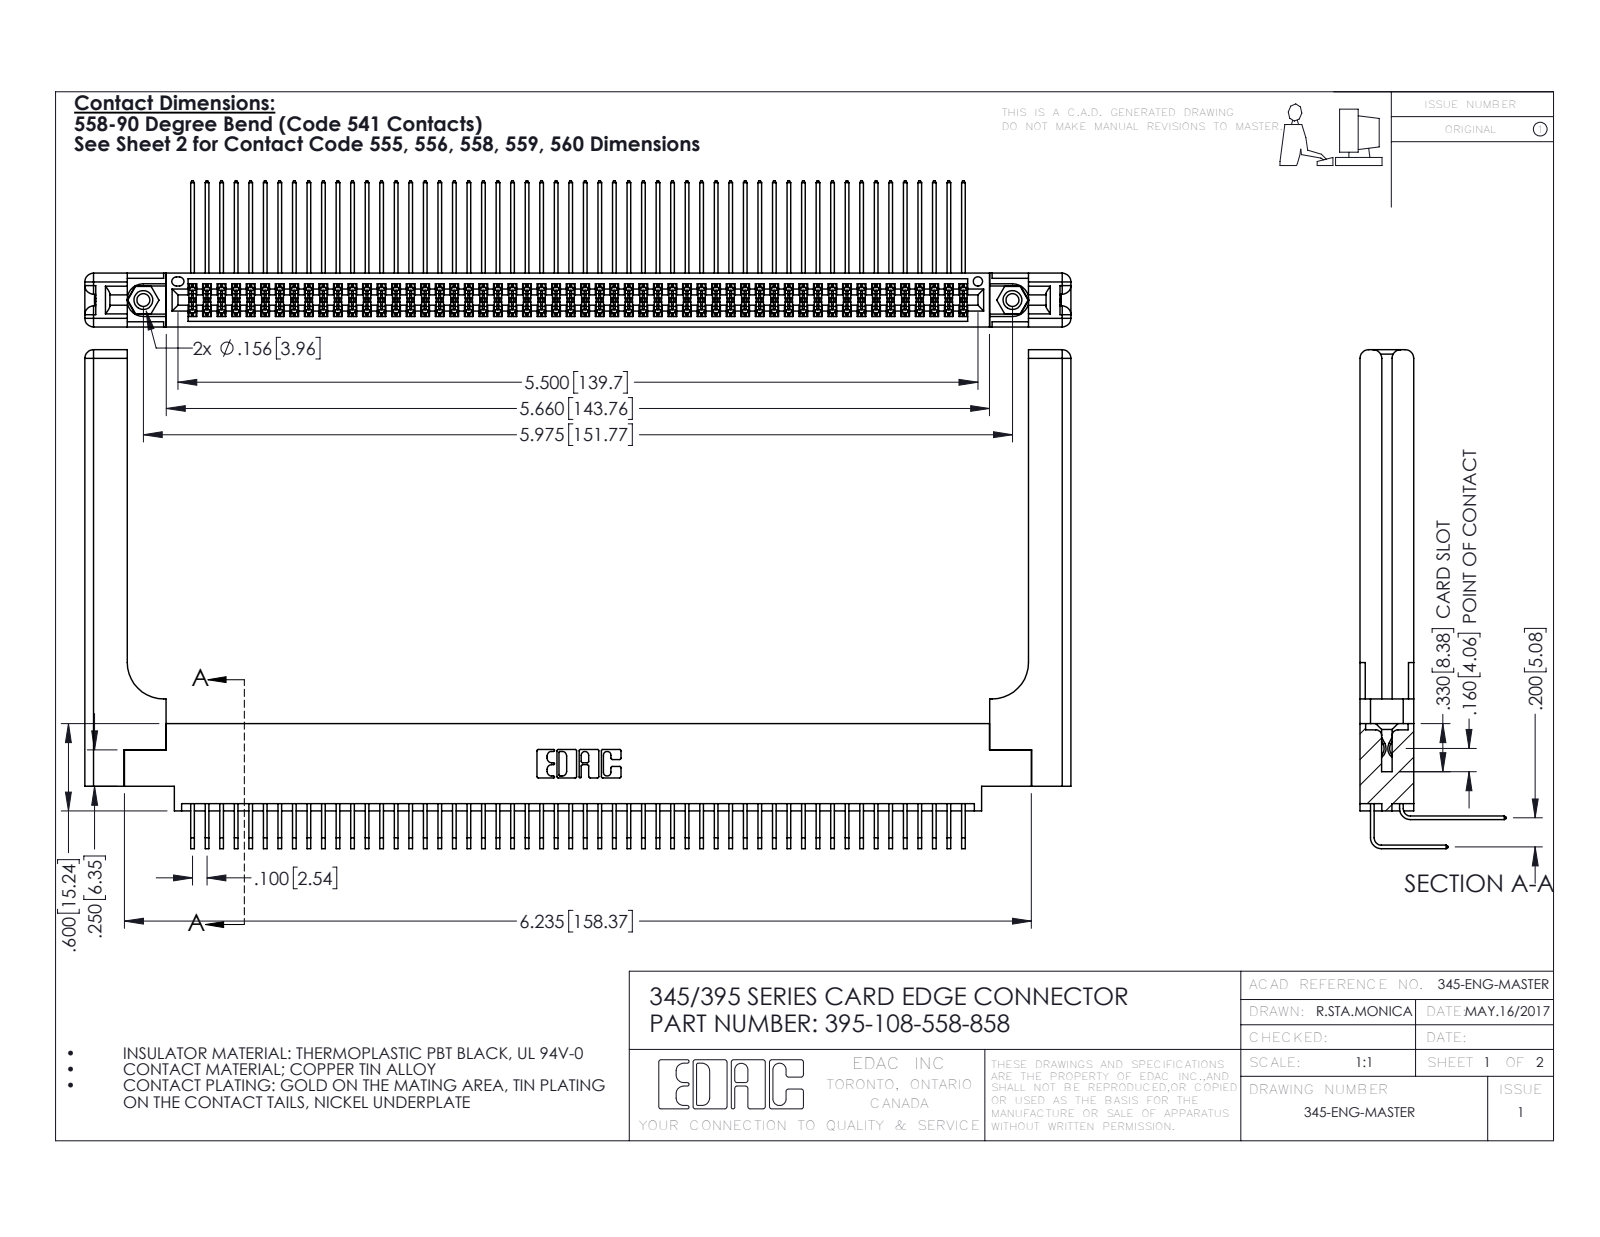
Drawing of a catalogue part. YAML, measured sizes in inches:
part_name: "395-108-558-858; 345-250-001_345-250-001-102; 345 Part_0.170 Offset - 0.156 Dia-TH; 345-292-001_558 559 Tail - 1 (+2 more)"
step_written_by: "SolidWorks 2016 (CONFIG_CONTROL_DESIGN)"
units: inches
bodies: {solids: 113, faces: 6002, planar: 4012, cylindrical: 1930, other: 60}
overall_size: [6.779, 3.429, 1.005]
volume: 1.576
surface_area: 52.71
round_holes:
  - {diameter: 0.089, count: 2}
  - {diameter: 0.125, count: 2}
  - {diameter: 0.156, count: 2}
  - {diameter: 0.064, count: 1}
round_bosses_or_shafts:
  - {diameter: 0.155, count: 2}
partial_cylinders:
  - {radius: 0.006, count: 163}
  - {radius: 0.01, count: 22}
  - {radius: 0.06, count: 16}
  - {radius: 0.007, count: 6}
  - {radius: 0.031, count: 6}
  - {radius: 0.026, count: 3}
  - {radius: 0.014, count: 2}
  - {radius: 0.019, count: 2}
face_to_face_distances: [0.072, 0.298, 0.37, 0.2, 0.098, 0.272, 0.025, 0.225, 0.175, 0.148]
hole_center_spacings: [0.27, 5.739, 5.975]
